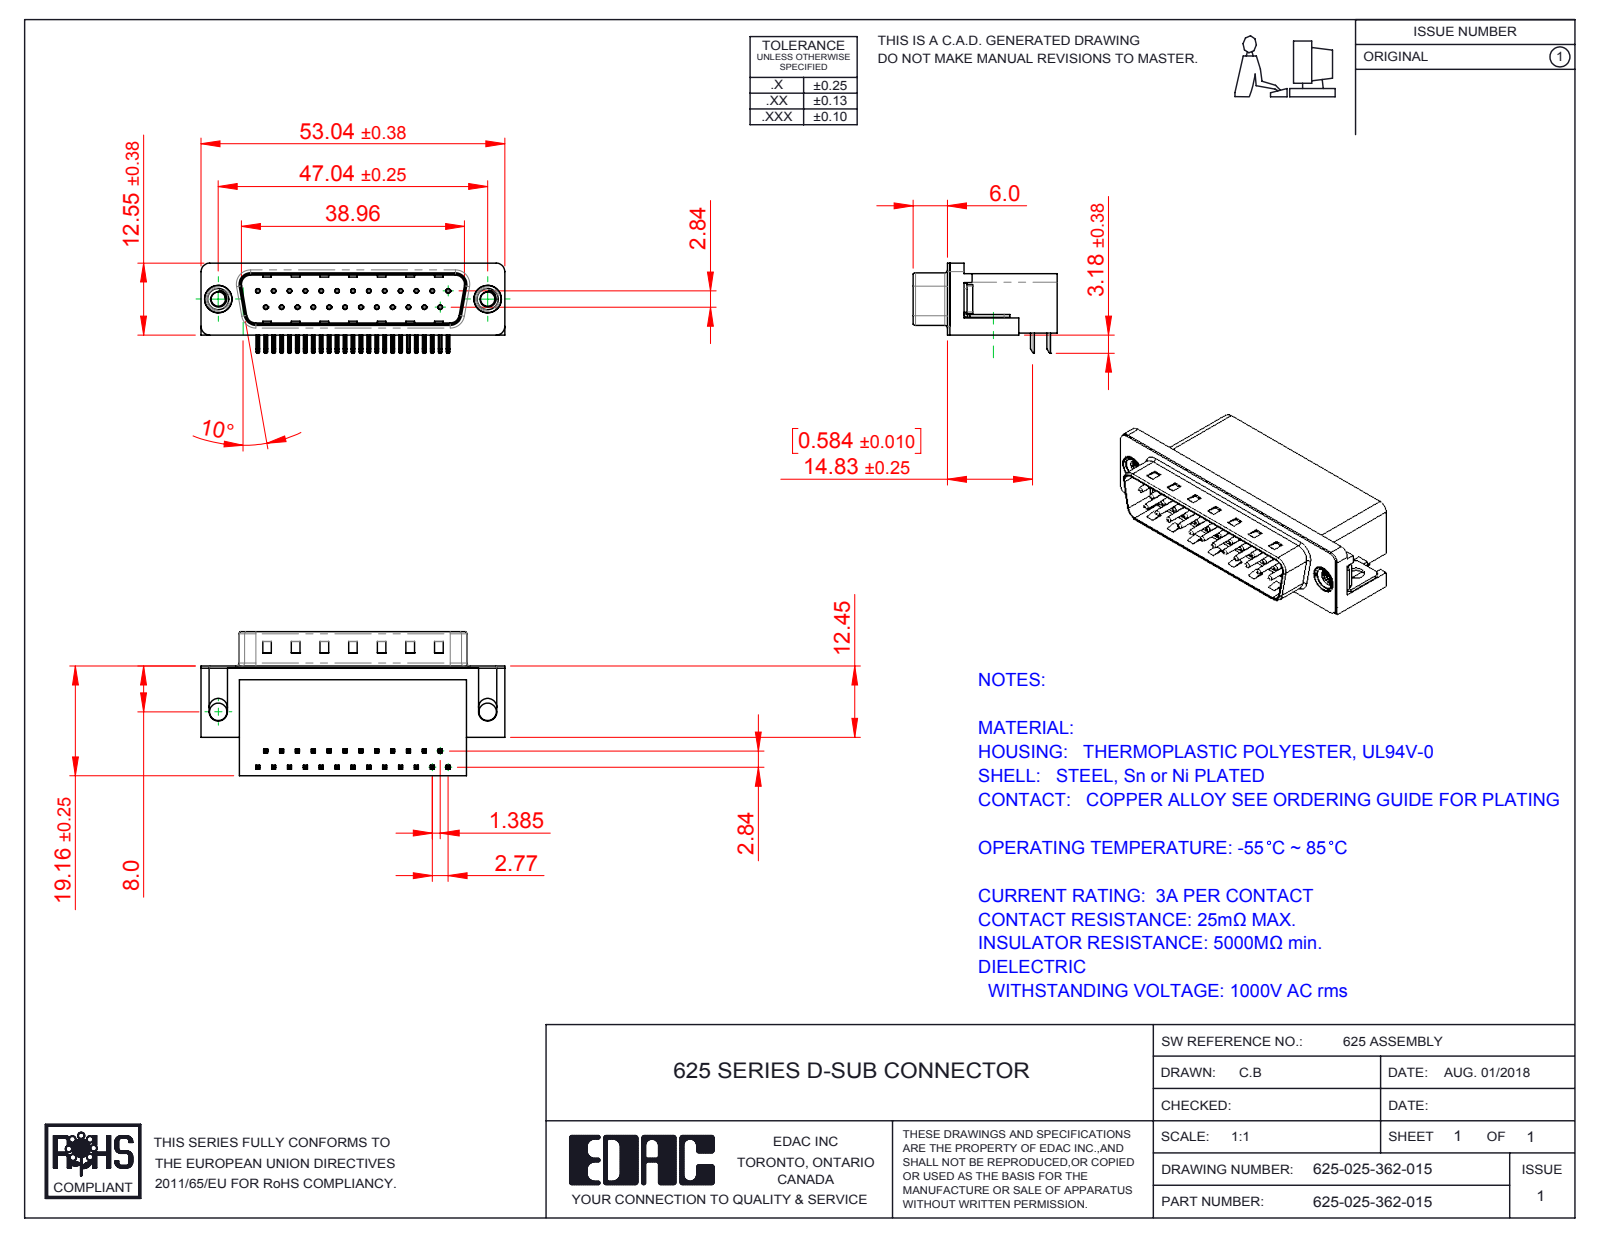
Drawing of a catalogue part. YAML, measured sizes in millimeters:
part_name: "625 M3 Threaded Rivet; 625 Housing_25 Socket; 625 Contact Bottom; 625-025-362-015 (+3 more)"
step_written_by: "SolidWorks 2016 (CONFIG_CONTROL_DESIGN)"
units: millimeters
bodies: {solids: 31, faces: 2265, planar: 1405, cylindrical: 665, other: 195}
overall_size: [53.04, 25.16, 15.73]
volume: 9157
surface_area: 8852
round_holes:
  - {diameter: 0.35, count: 25}
  - {diameter: 0.8, count: 25}
  - {diameter: 2.5, count: 2}
  - {diameter: 3.05, count: 2}
  - {diameter: 4, count: 2}
  - {diameter: 4.8, count: 2}
  - {diameter: 5, count: 2}
round_bosses_or_shafts:
  - {diameter: 0.75, count: 25}
  - {diameter: 4.9, count: 2}
  - {diameter: 4.75, count: 2}
  - {diameter: 3.9, count: 2}
partial_cylinders:
  - {radius: 0.25, count: 108}
  - {radius: 0.12, count: 50}
  - {radius: 1, count: 16}
  - {radius: 0.5, count: 9}
  - {radius: 1.6, count: 8}
  - {radius: 1.5, count: 7}
  - {radius: 0.9, count: 4}
  - {radius: 2, count: 4}
face_to_face_distances: [0.4, 10.35, 18.76, 2.1, 8.76, 10.46, 10.86, 1.7, 19.16, 10.11]
hole_center_spacings: [3.16, 2.77, 11.08, 5.54, 8.31, 5.03, 13.85, 7.48]
